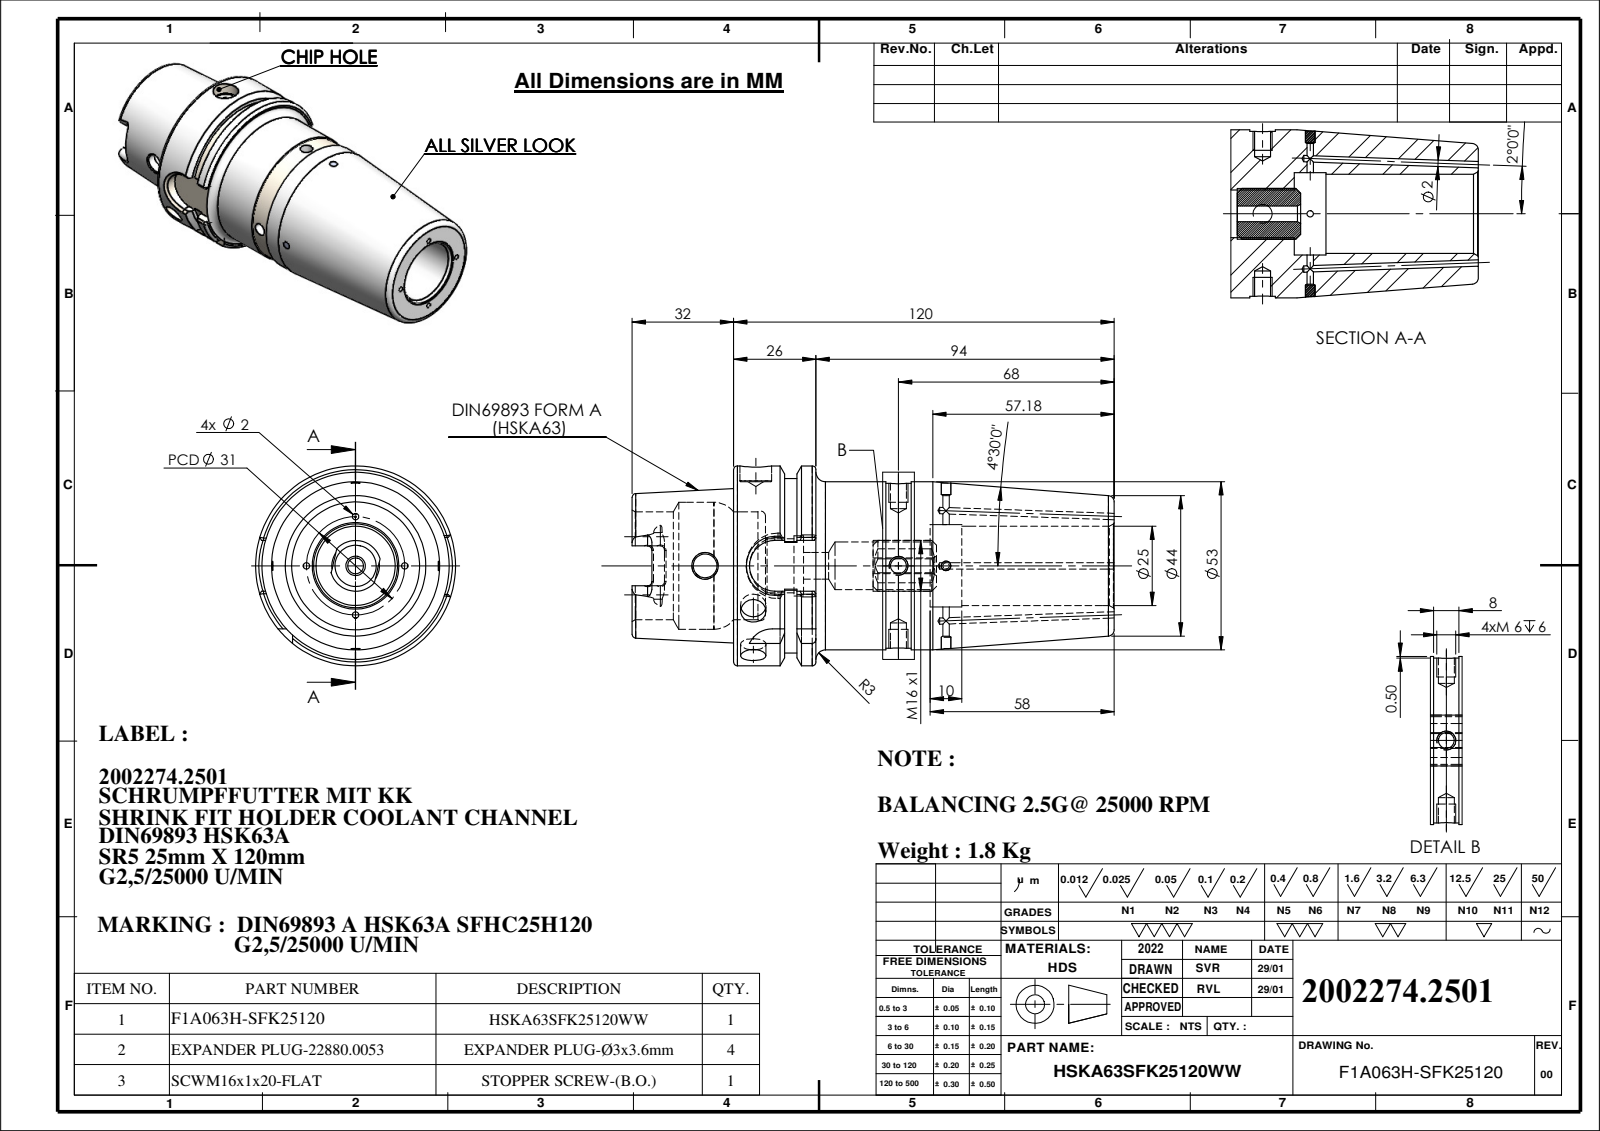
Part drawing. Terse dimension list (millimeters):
name: SCWM16X1X20-FLAT; HSKA63SFK25120WW; 9163A-SR525120; EXPANDER PLUG Ø3x3.6
written by: SolidWorks 2018 (CONFIG_CONTROL_DESIGN)
unit: mm
bodies: 6 solids, 286 faces (70 planar, 118 cylindrical, 98 other)
size: 151.95 × 63 × 63
volume: 234 796 mm³; area: 46 628 mm²
holes: 6× ⌀2, 3× ⌀5, 2× ⌀3, 2× ⌀8, 1× ⌀7.5, 1× ⌀8.4, 1× ⌀10, 1× ⌀15, 1× ⌀17, 1× ⌀19, 1× ⌀24.99, 1× ⌀25.99
bosses: 1× ⌀63, 1× ⌀55, 1× ⌀53, 1× ⌀52
rounds: 6× R1.3, 4× R2.88, 3× R8, 1× R9
face distances: 119.95, 10, 109.95, 61.95, 32, 42, 151.95, 93.95, 51.95, 58
hole spacings: 15, 44.95, 59.95, 60.95, 75.95
